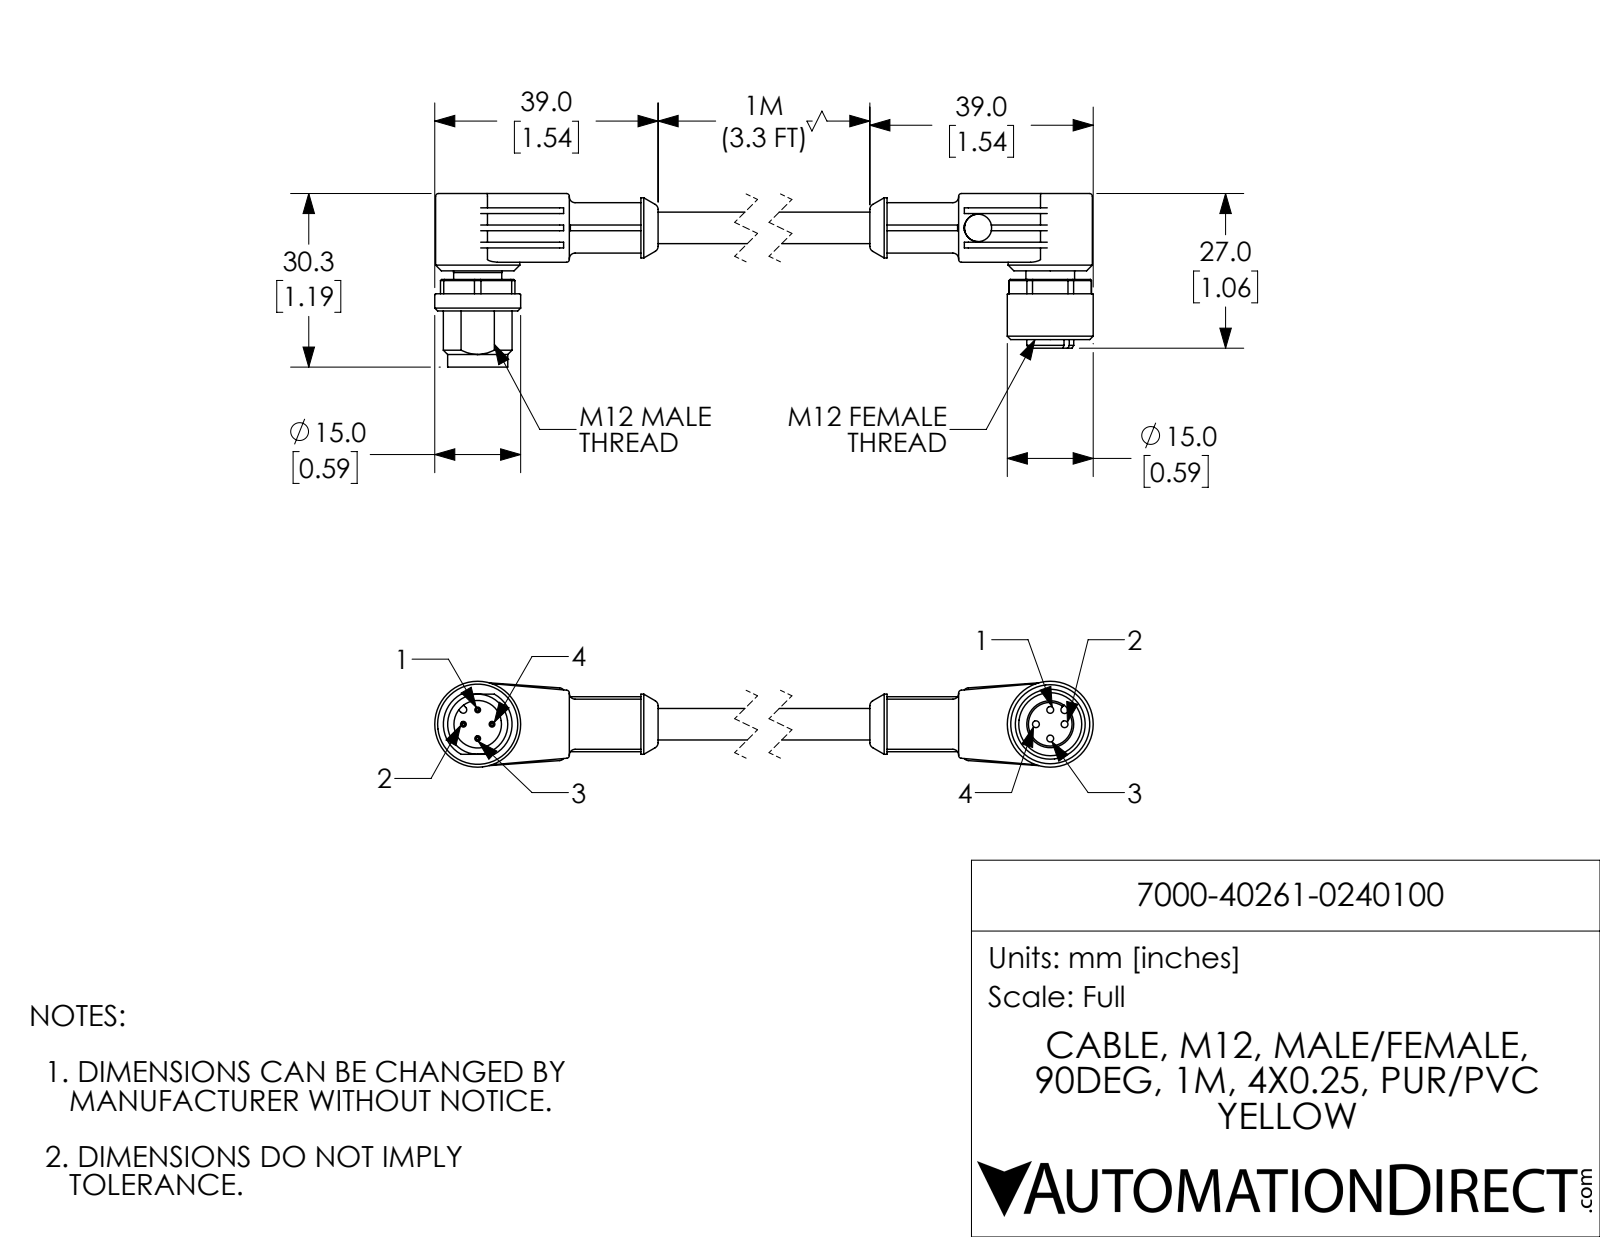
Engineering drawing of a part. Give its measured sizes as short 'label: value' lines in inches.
name: 7000-40261-0240100_FEMALE; 7000-40261-0240100; 7000-40261-0240100_MALE
written by: SolidWorks 2017 (AUTOMOTIVE_DESIGN)
unit: in
bodies: 2 solids, 290 faces (123 planar, 104 cylindrical, 63 other)
size: 5.118 × 1.193 × 0.591
volume: 0.829 in³; area: 10.88 in²
holes: 4× ⌀0.047, 2× ⌀0.189, 1× ⌀0.327, 1× ⌀0.433
bosses: 4× ⌀0.039, 2× ⌀0.591, 2× ⌀0.579, 2× ⌀0.413, 1× ⌀0.346, 1× ⌀0.335, 1× ⌀0.333, 1× ⌀0.331
rounds: 16× R0.02, 4× R0.039, 2× R0.283, 1× R0.024, 1× R0.026, 1× R0.236
face distances: 0.472, 0.059, 0.118, 0.591, 0.531, 0.178, 0.217, 0.098, 0.374, 0.256
hole spacings: 0.098, 0.139, 0.197, 4.529, 3.563, 4.429, 4.528, 4.626
